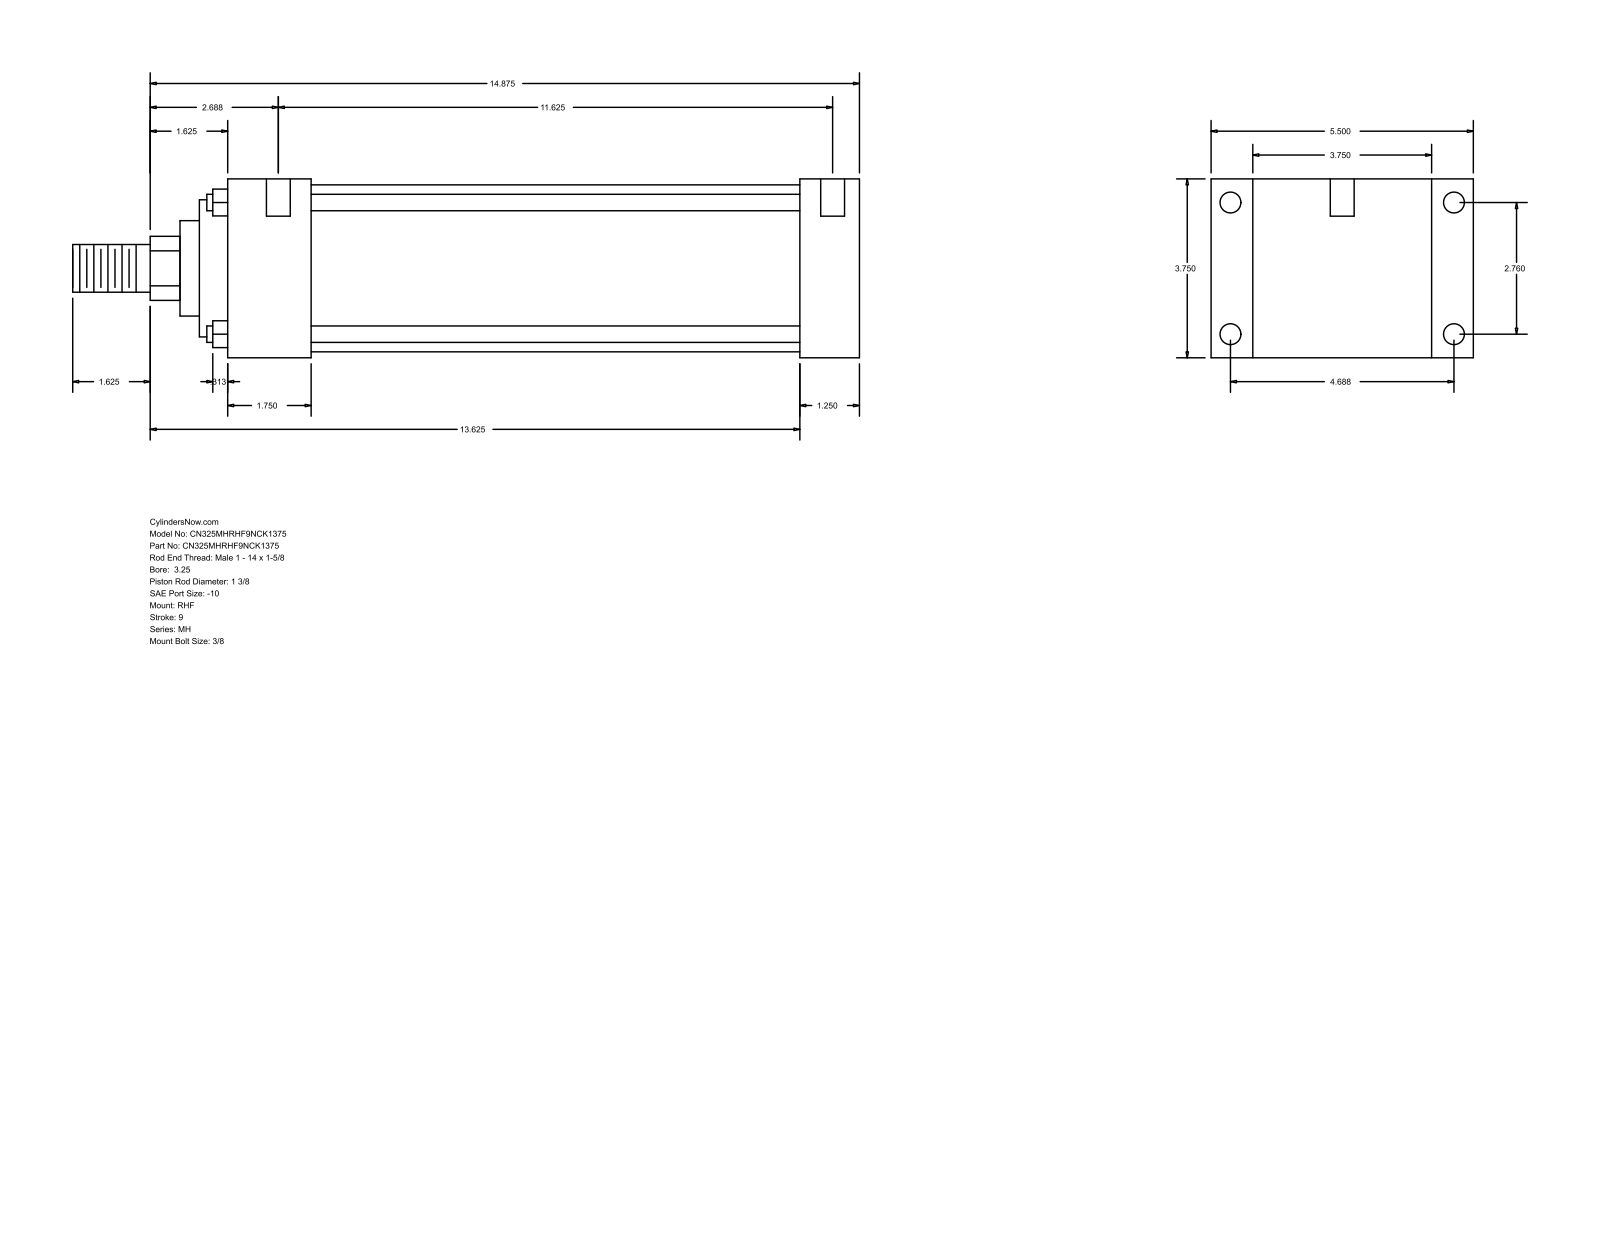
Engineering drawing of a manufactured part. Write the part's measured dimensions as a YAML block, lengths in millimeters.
part_name: "MH_RHF__0325_1.375"
step_written_by: "GSSL Pune (CONFIG_CONTROL_DESIGN)"
units: millimeters
bodies: {solids: 0, faces: 90, planar: 61, cylindrical: 29, other: 0}
overall_size: [419.1, 139.7, 95.25]
round_holes:
  - {diameter: 5.56, count: 4}
  - {diameter: 11.13, count: 4}
  - {diameter: 12.7, count: 2}
round_bosses_or_shafts:
  - {diameter: 8.76, count: 4}
  - {diameter: 88.9, count: 1}
  - {diameter: 73.03, count: 1}
  - {diameter: 50.8, count: 1}
  - {diameter: 34.92, count: 1}
  - {diameter: 25.4, count: 1}
partial_cylinders:
  - {radius: 17.06, count: 1}
face_to_face_distances: [95.24, 31.75, 22.23, 117.47, 304.8, 336.55, 139.7, 44.45, 260.35, 292.1]
hole_center_spacings: [70.1, 119.06, 138.16, 301.63, 1.59, 4.76, 295.28, 296.87]
